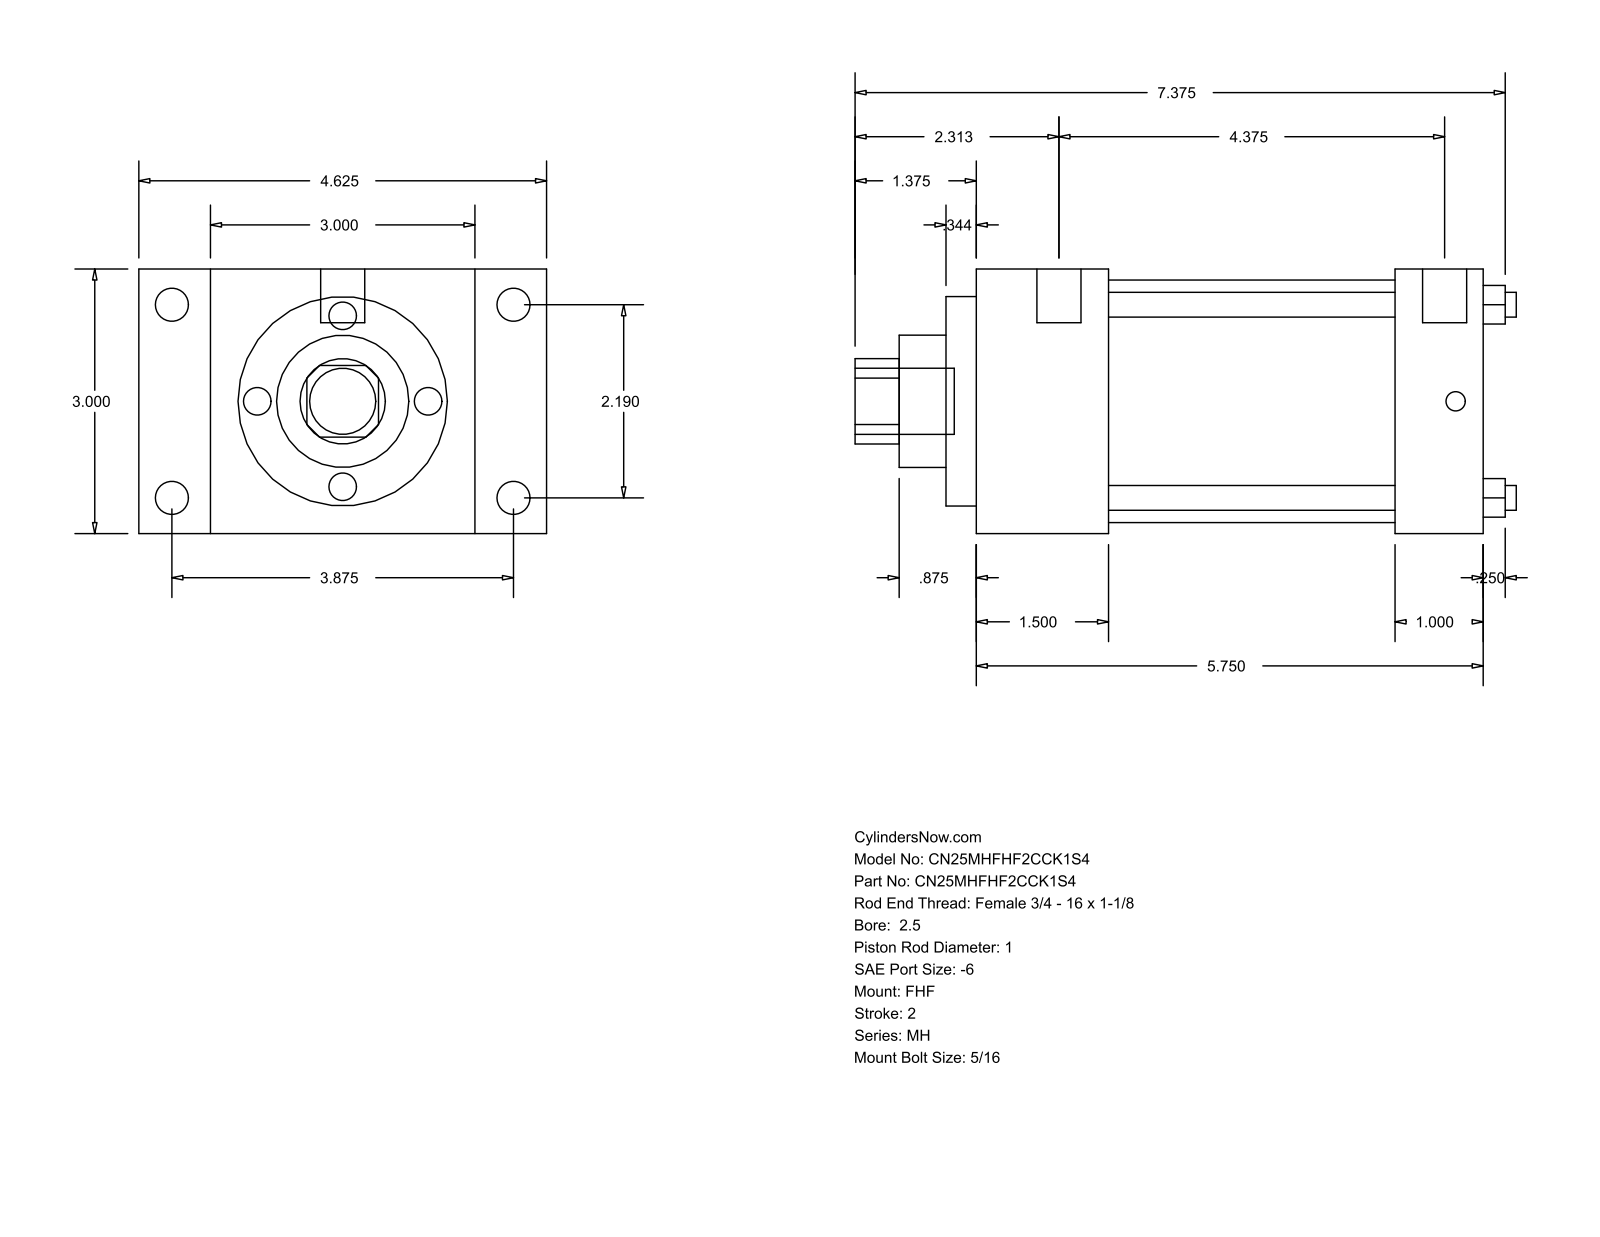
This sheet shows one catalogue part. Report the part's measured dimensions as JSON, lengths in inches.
{"part_name": "MH_FHF__0250_1", "step_written_by": "GSSL Pune (CONFIG_CONTROL_DESIGN)", "units": "inches", "bodies": {"solids": 0, "faces": 90, "planar": 61, "cylindrical": 29, "other": 0}, "overall_size": [7.5, 4.625, 3], "round_holes": [[0.281, 4], [1, 1], [1.5, 1], [2.375, 1], [2.75, 1]], "round_bosses_or_shafts": [[0.375, 4], [0.219, 4], [0.5, 2], [0.75, 1]], "partial_cylinders_radius": [[0.484, 1]], "face_to_face_distances": [3, 5.75, 1.5, 4.25, 0.813, 3.813, 4.625, 4.75, 3.25, 1], "hole_center_spacings": [1.548, 2.19, 3.097]}
